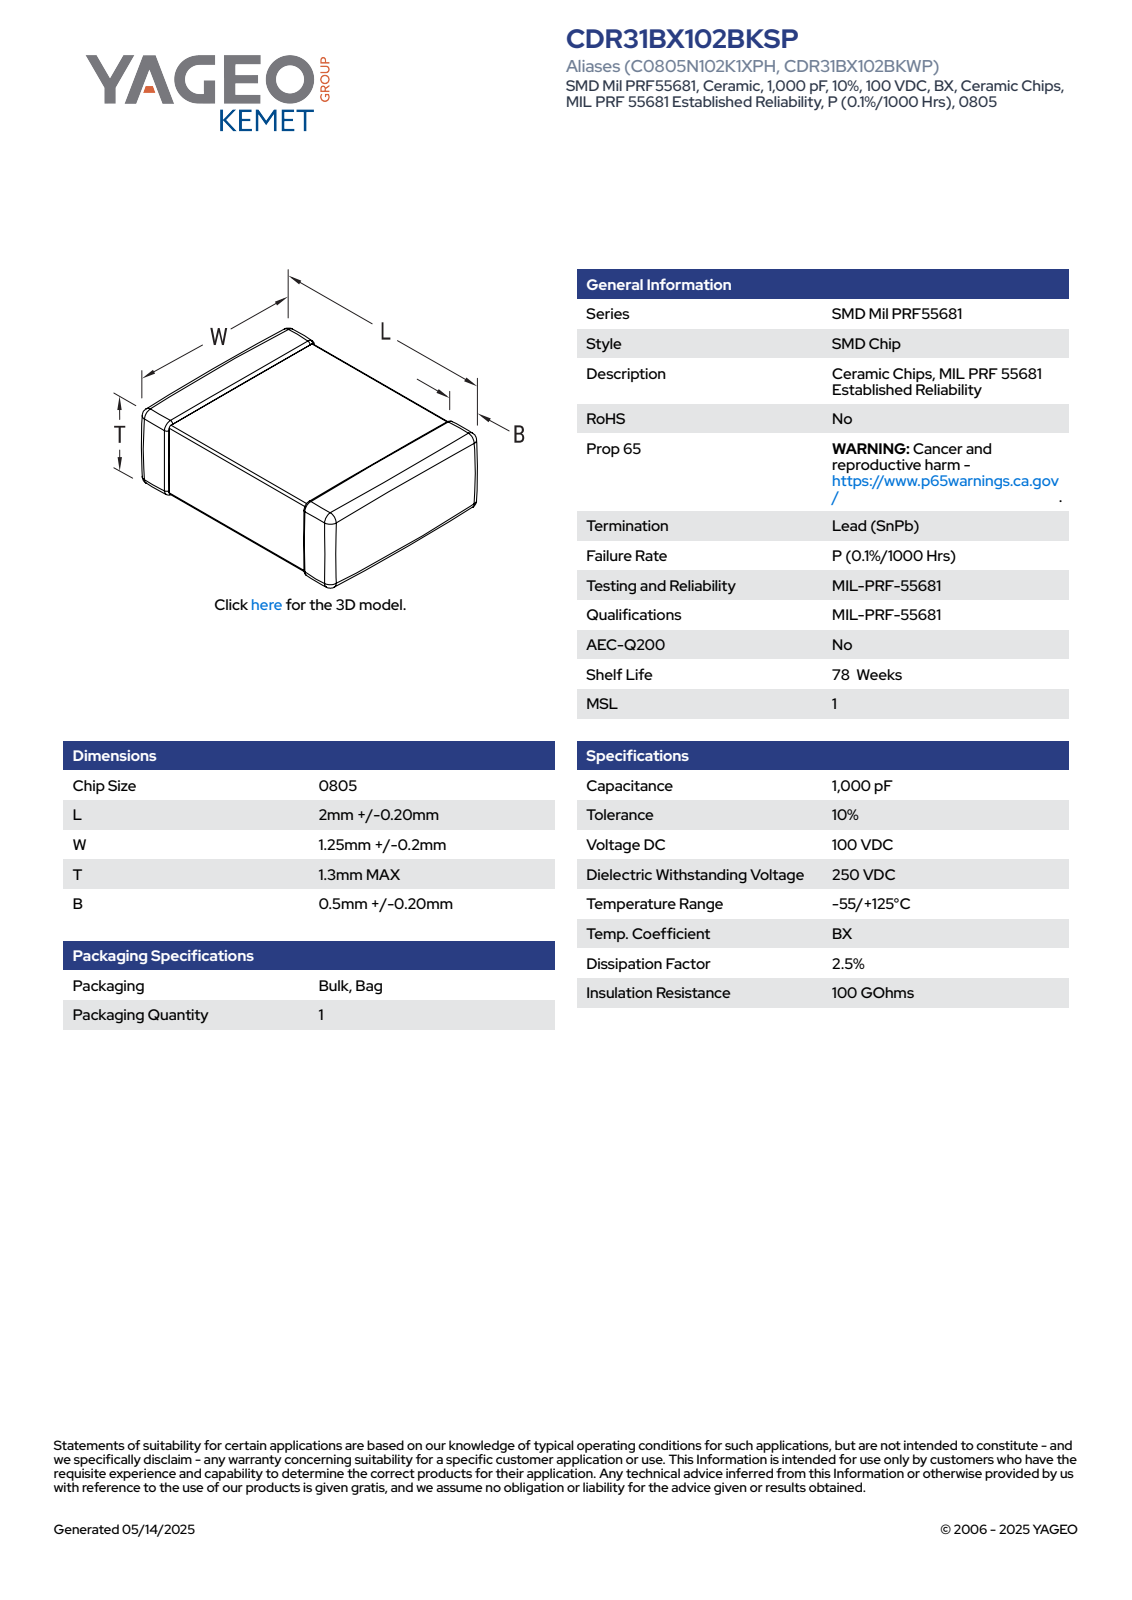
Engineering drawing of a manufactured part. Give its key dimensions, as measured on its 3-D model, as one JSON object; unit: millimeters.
{"part_name": "CCS_STDNOS_0805_L2.2W1.45T1.3B0.5", "step_written_by": "SolidWorks 2021 (AUTOMOTIVE_DESIGN)", "units": "millimeters", "bodies": {"solids": 4, "faces": 125, "planar": 71, "cylindrical": 38, "other": 16}, "overall_size": [2.2, 1.45, 1.3], "volume_mm3": 4, "surface_area_mm2": 16, "face_to_face_distances": [1.27, 1.42, 2.2, 1.3, 1.45, 1.24, 1.39, 0.7, 0.72, 0.75]}
